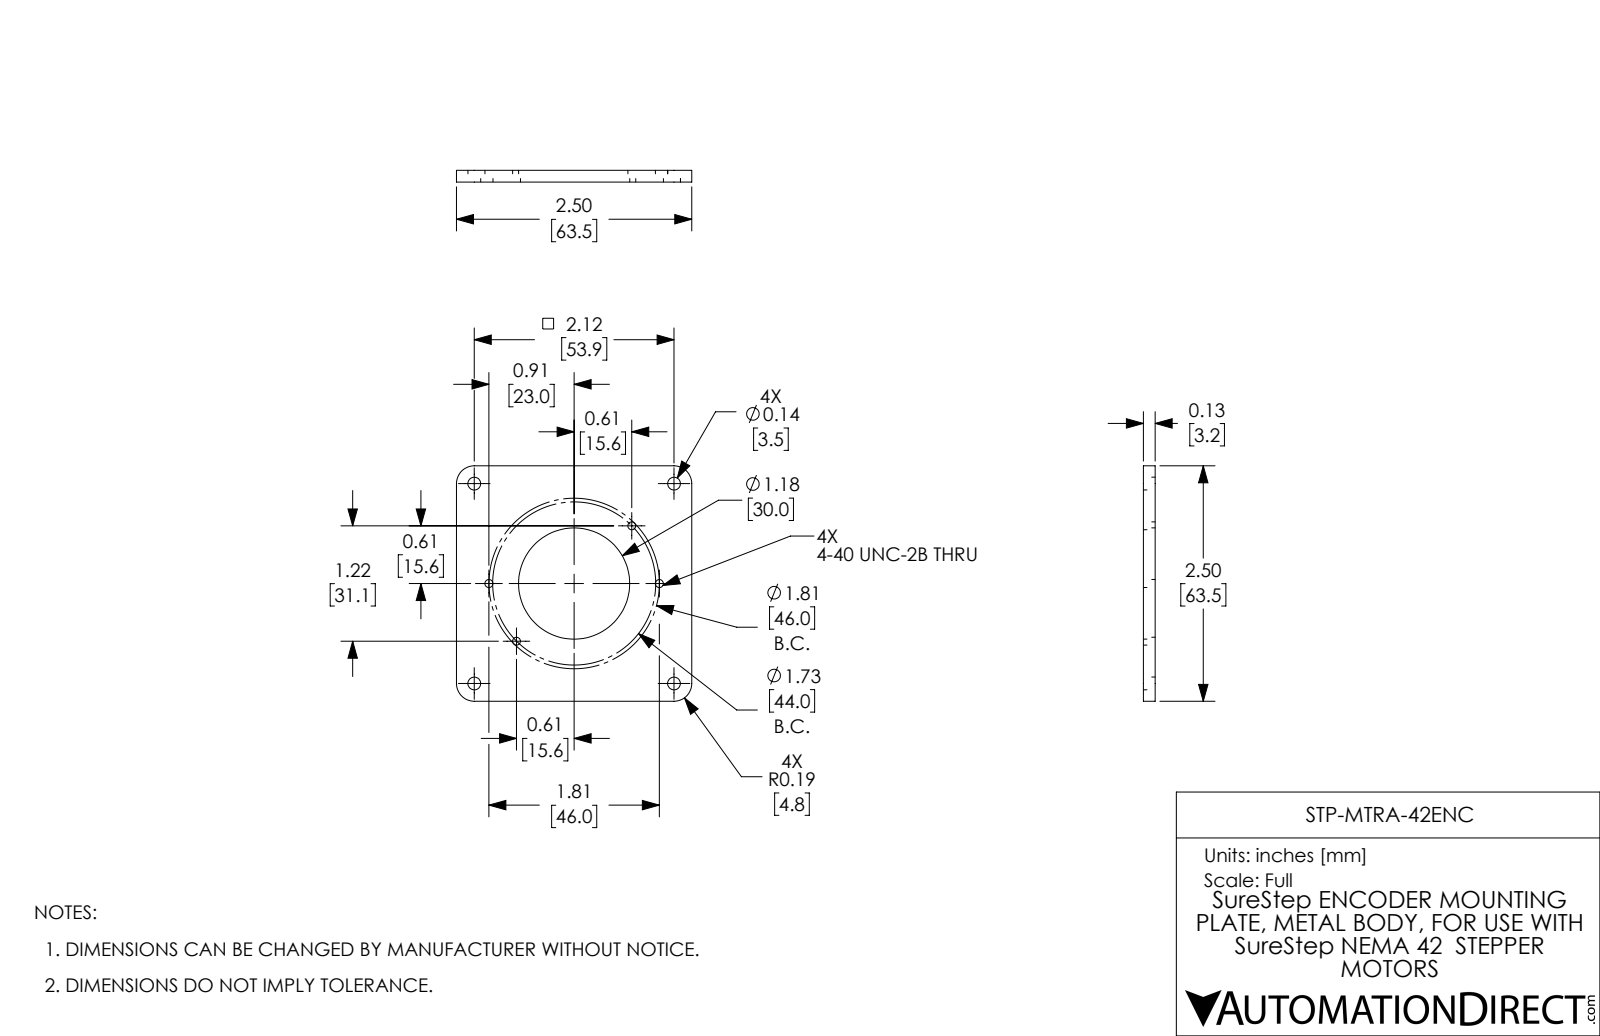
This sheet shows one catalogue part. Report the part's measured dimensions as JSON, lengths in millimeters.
{"part_name": "STP-MTRA-42ENC", "step_written_by": "SolidWorks 2017 (AUTOMOTIVE_DESIGN)", "units": "millimeters", "bodies": {"solids": 1, "faces": 28, "planar": 6, "cylindrical": 22, "other": 0}, "overall_size": [63.5, 63.5, 3.18], "volume_mm3": 10347, "surface_area_mm2": 7812, "round_holes": [[3.45, 4], [2.12, 2], [2.17, 2], [30, 1]], "partial_cylinders_radius": [[4.8, 4]], "face_to_face_distances": [3.18, 63.5], "hole_center_spacings": [44.01, 27.24, 38.11, 53.9, 56.76, 17.25, 22.01, 23]}
